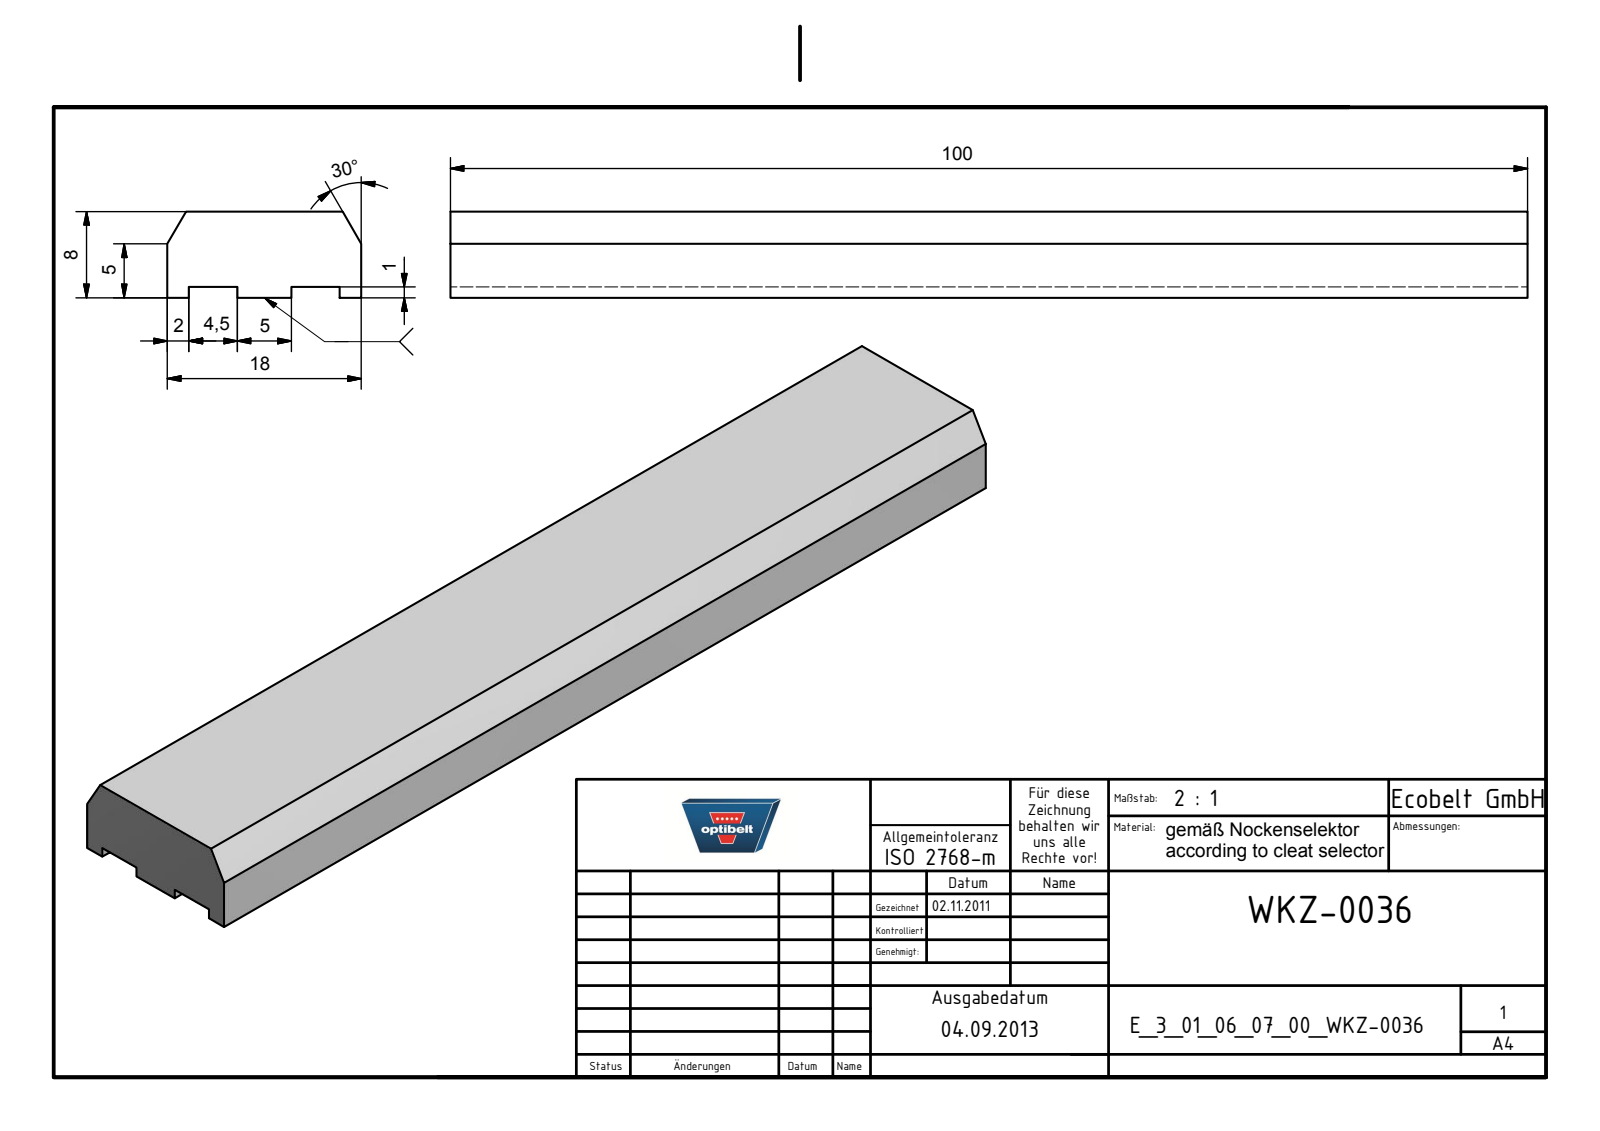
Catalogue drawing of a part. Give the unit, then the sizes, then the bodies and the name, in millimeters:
Units: millimetres
Overall size (bounding box): 100 × 18 × 8
Main face-to-face distances: 1, 8, 7, 18, 2, 16, 6.5, 11.5, 4.5, 9.5
Volume: 12 980 mm³ · Surface area: 5 606 mm²
Bodies: 1 solid, 16 faces (16 planar, 0 cylindrical, 0 other)
Part name (STEP PRODUCT): E_3_01_06_07_00_WKZ-0036
STEP written by: Autodesk Inventor 2021 (AUTOMOTIVE_DESIGN)
